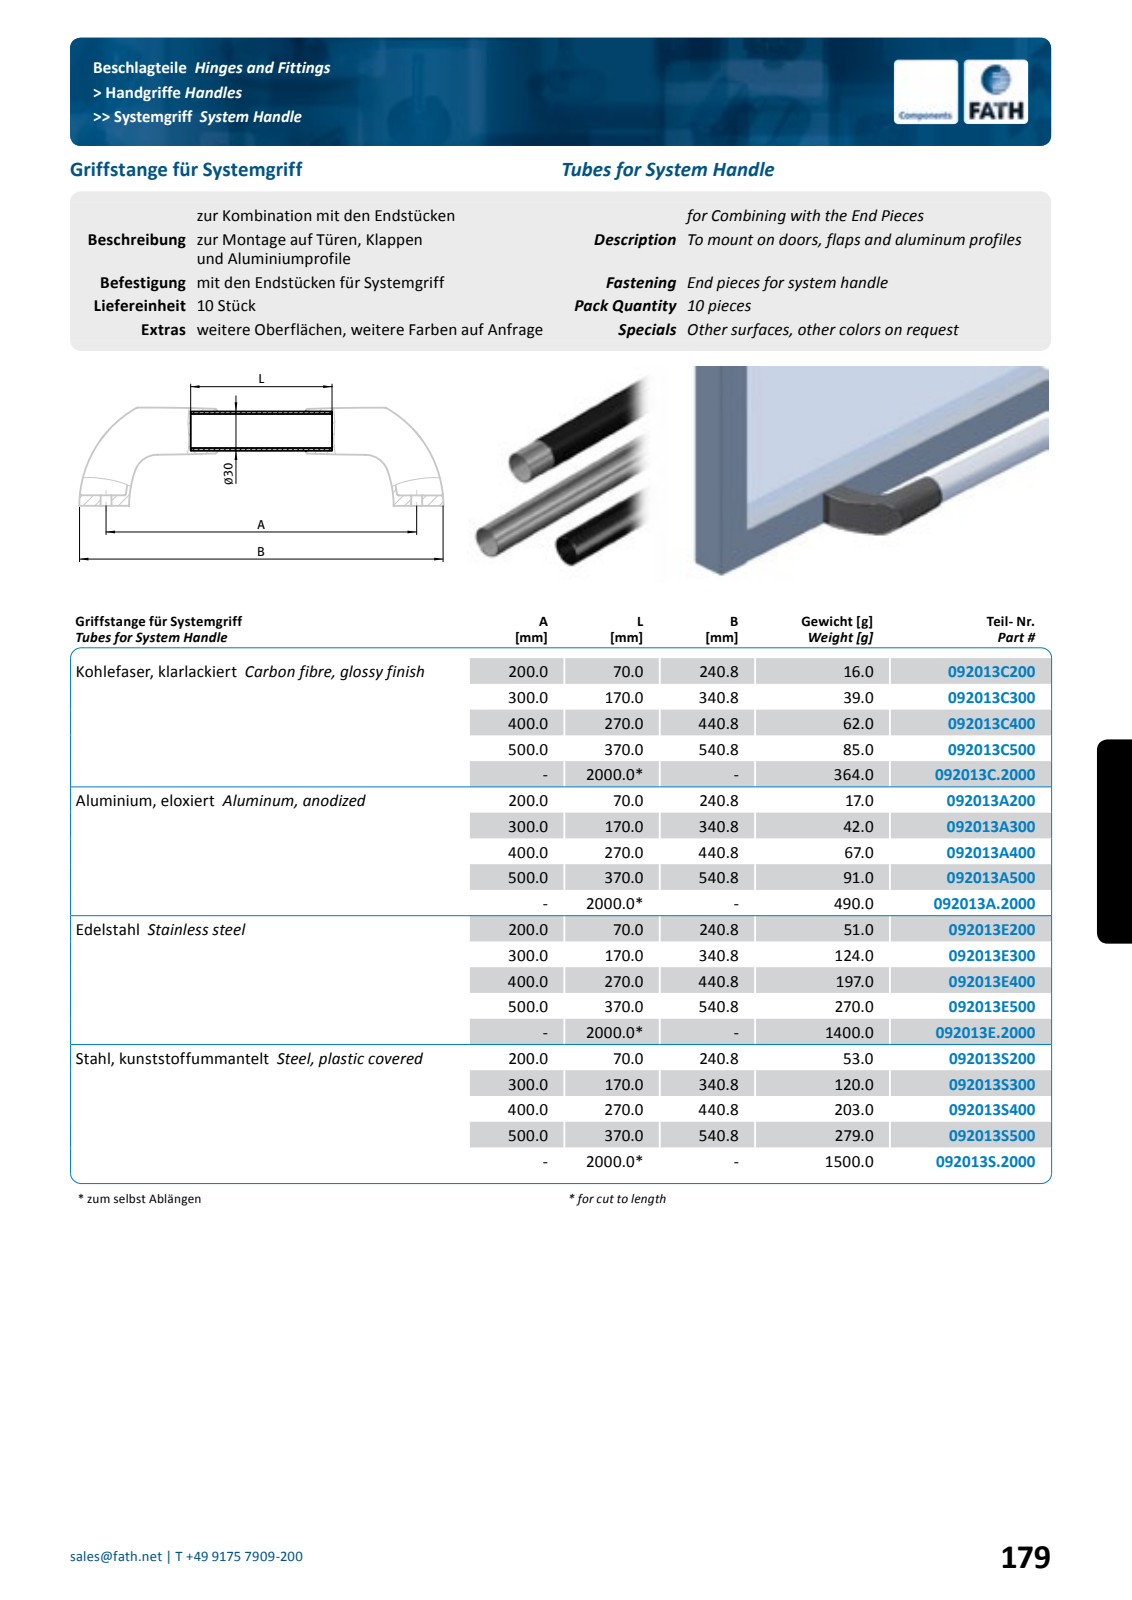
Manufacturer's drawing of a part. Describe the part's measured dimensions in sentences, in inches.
The part is named "fath_092013s500". Its 3-D file was written by "Spatial InterOp 3D (automotive_design)". It is 1 solid with 6 faces: 2 planar, 4 cylindrical and 0 other. Overall it measures 14.567 by 1.181 by 1.181 inches. Its volume is 2.057 cubic inches and its surface area 104.8 square inches. Round holes: 1 of diameter 1.102. Round bosses or shafts: 1 of diameter 1.181. The main face-to-face distances are 14.567.
